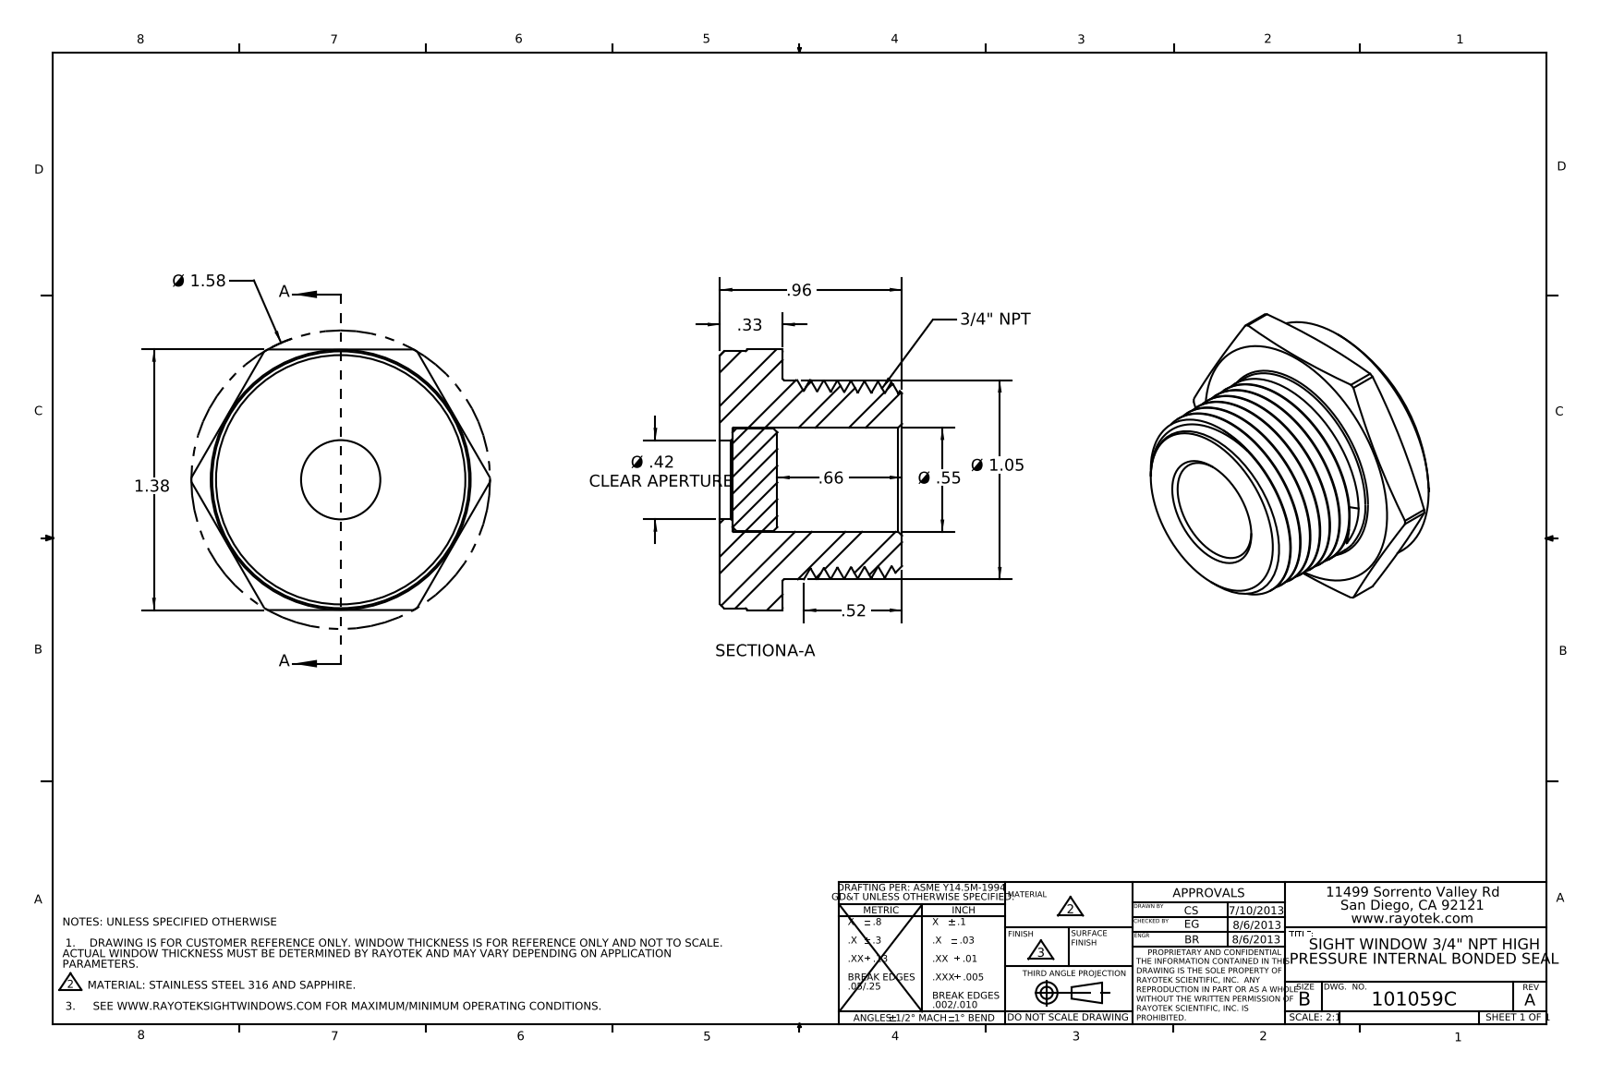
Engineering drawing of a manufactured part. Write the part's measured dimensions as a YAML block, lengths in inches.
part_name: "101059; 402059; 403059"
step_written_by: "SolidWorks 2012 (AUTOMOTIVE_DESIGN)"
units: inches
bodies: {solids: 2, faces: 72, planar: 15, cylindrical: 17, other: 40}
overall_size: [1.576, 1.375, 0.96]
volume: 0.828
surface_area: 9.962
round_holes:
  - {diameter: 0.418, count: 1}
  - {diameter: 0.55, count: 1}
round_bosses_or_shafts:
  - {diameter: 1.355, count: 1}
  - {diameter: 1.05, count: 1}
  - {diameter: 0.54, count: 1}
partial_cylinders:
  - {radius: 0.788, count: 1}
face_to_face_distances: [0.33, 1.375, 0.96, 0.63, 0.066, 0.264, 0.894, 0.302, 0.236, 0.028]
